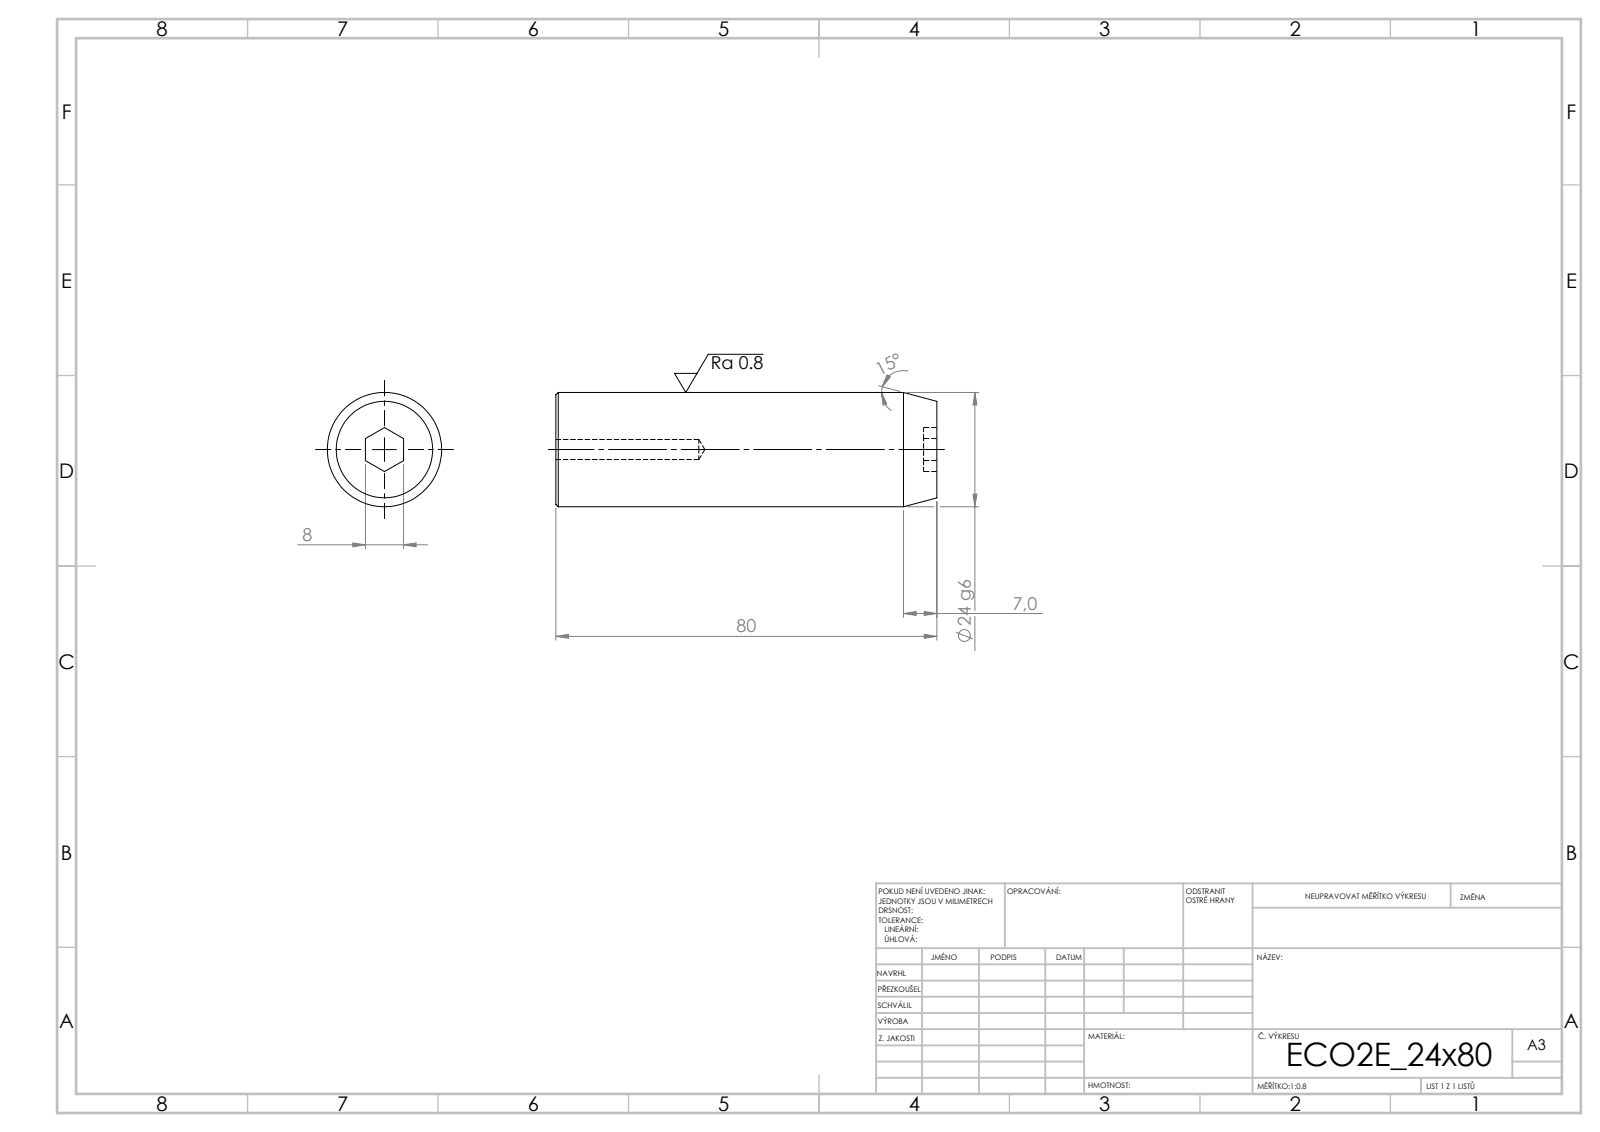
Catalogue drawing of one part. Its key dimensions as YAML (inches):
step_written_by: "SolidWorks 2019 (CONFIG_CONTROL_DESIGN)"
units: inches
bodies: {solids: 1, faces: 19, planar: 9, cylindrical: 4, other: 6}
overall_size: [3.15, 0.945, 0.945]
volume: 2.144
surface_area: 11.22
round_holes:
  - {diameter: 0.165, count: 1}
round_bosses_or_shafts:
  - {diameter: 0.945, count: 1}
face_to_face_distances: [3.15, 0.11, 3.039, 0.315]
